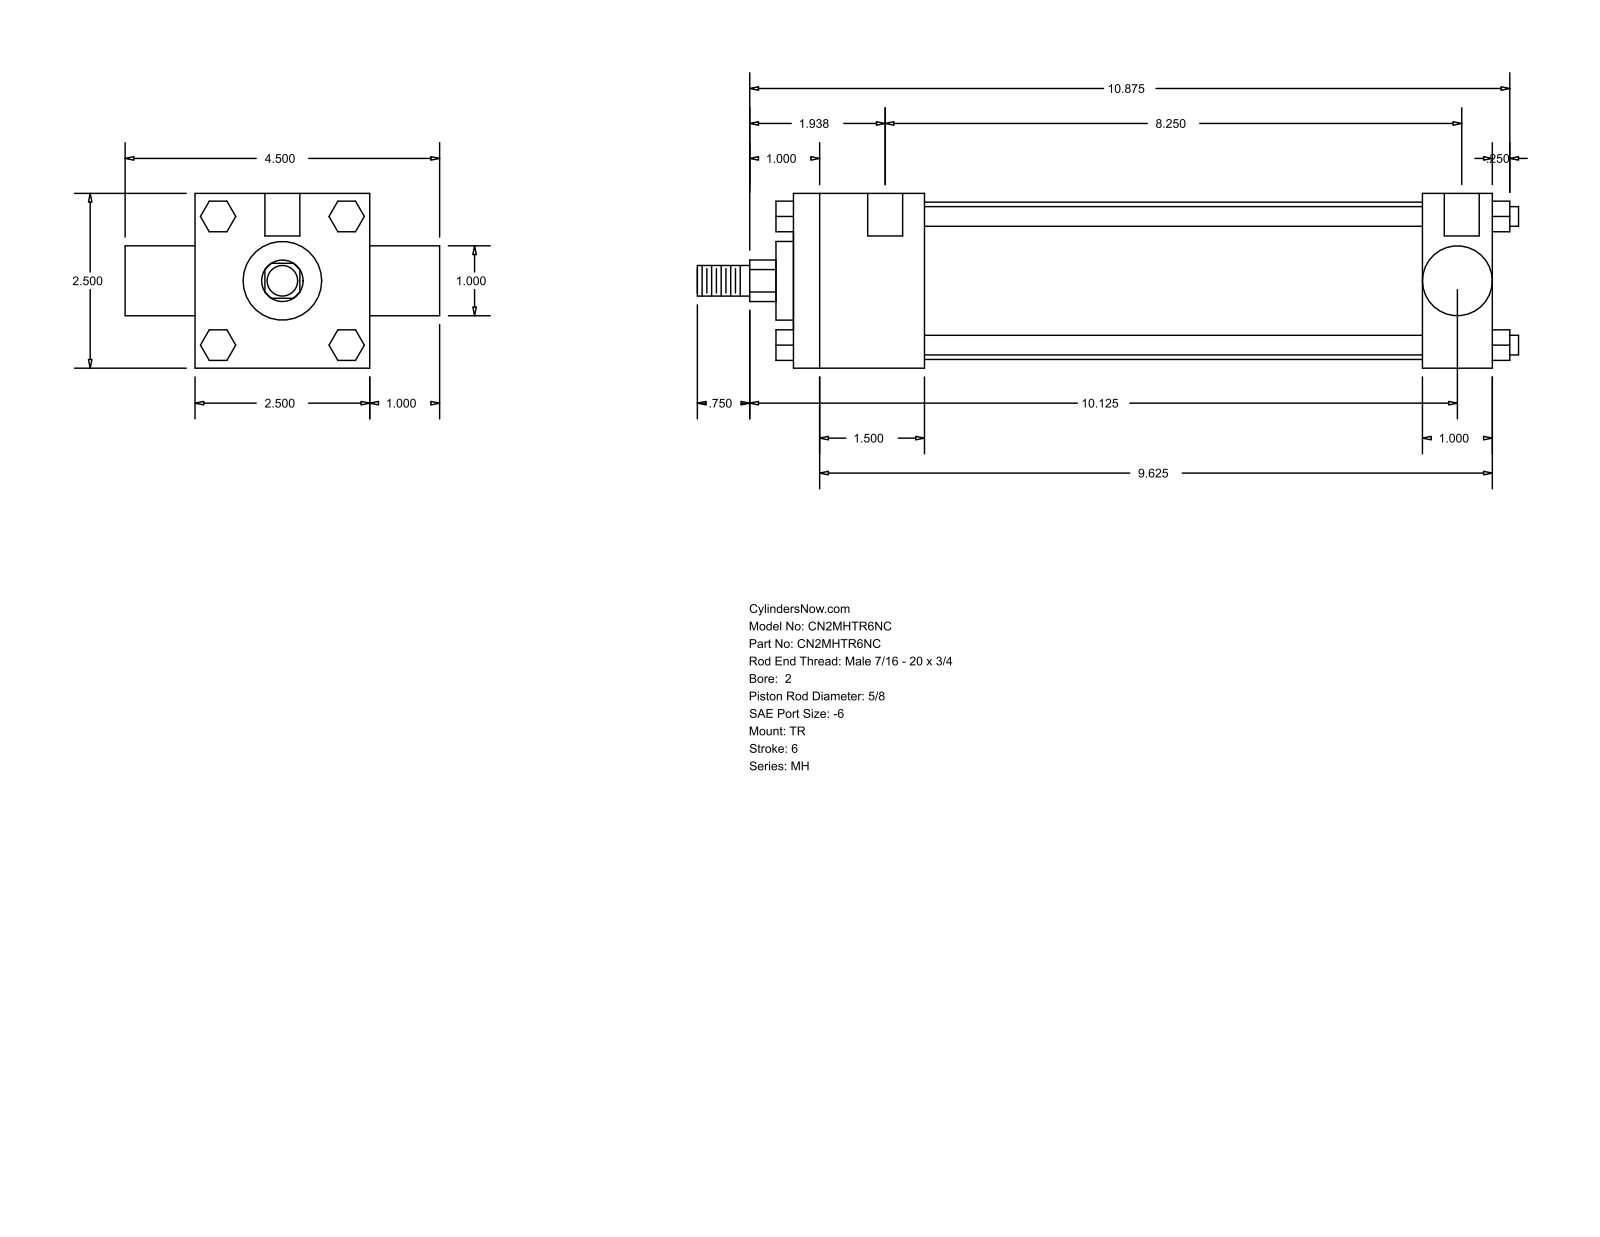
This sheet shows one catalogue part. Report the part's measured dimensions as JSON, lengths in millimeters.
{"part_name": "MH_TR__0200_0.625", "step_written_by": "GSSL Pune (CONFIG_CONTROL_DESIGN)", "units": "millimeters", "bodies": {"solids": 0, "faces": 120, "planar": 92, "cylindrical": 28, "other": 0}, "overall_size": [298.45, 114.3, 63.5], "round_holes": [[5.56, 3], [12.7, 2]], "round_bosses_or_shafts": [[7.14, 4], [57.15, 1], [28.57, 1], [25.35, 1], [15.88, 1], [11.11, 1]], "partial_cylinders_radius": [[7.54, 1]], "face_to_face_distances": [63.5, 254, 47.62, 228.59, 180.97, 206.38, 25.41, 25.4, 6.35, 88.9], "hole_center_spacings": [3.18, 4.76, 209.55, 212.73, 214.31, 217.49]}
